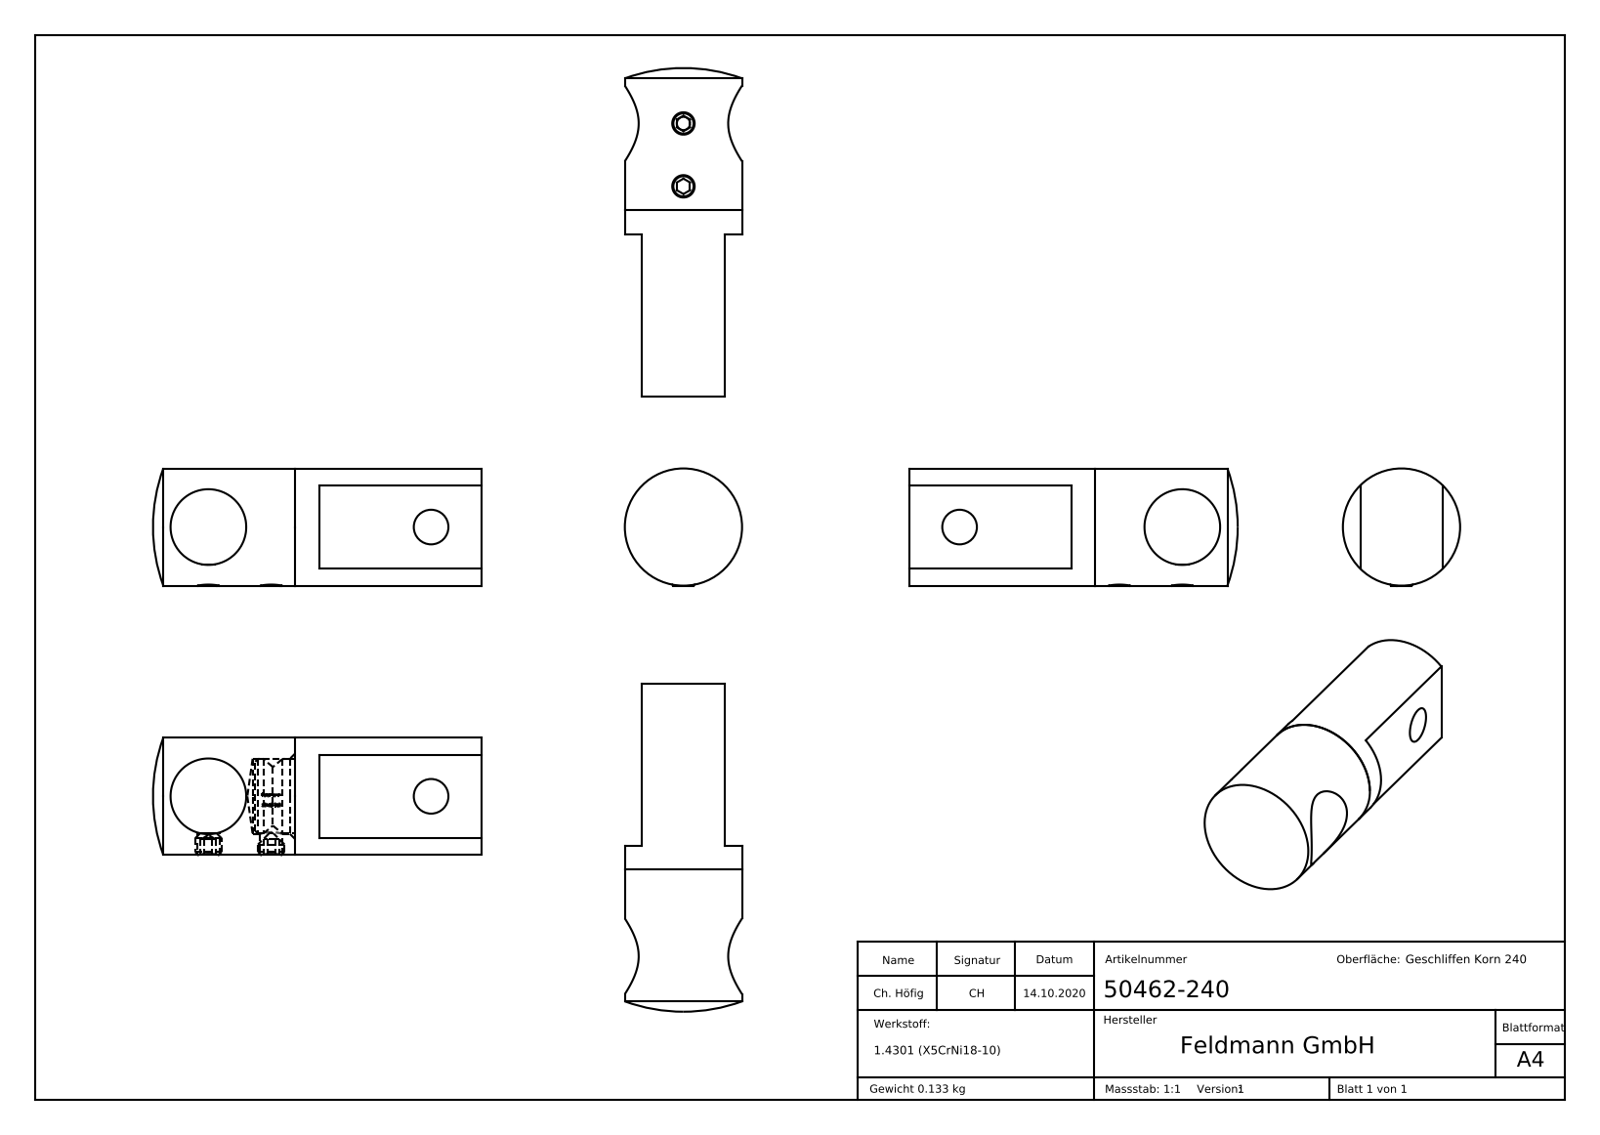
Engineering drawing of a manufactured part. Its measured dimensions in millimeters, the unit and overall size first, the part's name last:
Units: millimetres
Overall size (bounding box): 72 × 61.6 × 22
Round holes (diameter × count): ⌀4.2 ×2, ⌀6.5 ×1, ⌀14.1 ×1, ⌀14.2 ×1
Round bosses / shafts (diameter × count): ⌀5 ×2, ⌀22 ×1, ⌀14 ×1
Partial cylindrical surfaces — rounded edges, fillets, slot ends (radius × count): R7.15 ×1
Main face-to-face distances: 15.5, 34.9, 42.4, 7.5, 30.4, 4.5, 12, 2.5, 6.5, 9
Hole centre spacings: 11.8, 41.8
Volume: 16 814 mm³ · Surface area: 7 271 mm²
Bodies: 4 solids, 306 faces (136 planar, 53 cylindrical, 117 other)
Part name (STEP PRODUCT): DIN914; DIN913_DIN 913 M5x4; 5046X-240 Teil1; 50462-240 (+5 more)
STEP written by: SolidWorks 2018 (CONFIG_CONTROL_DESIGN)
